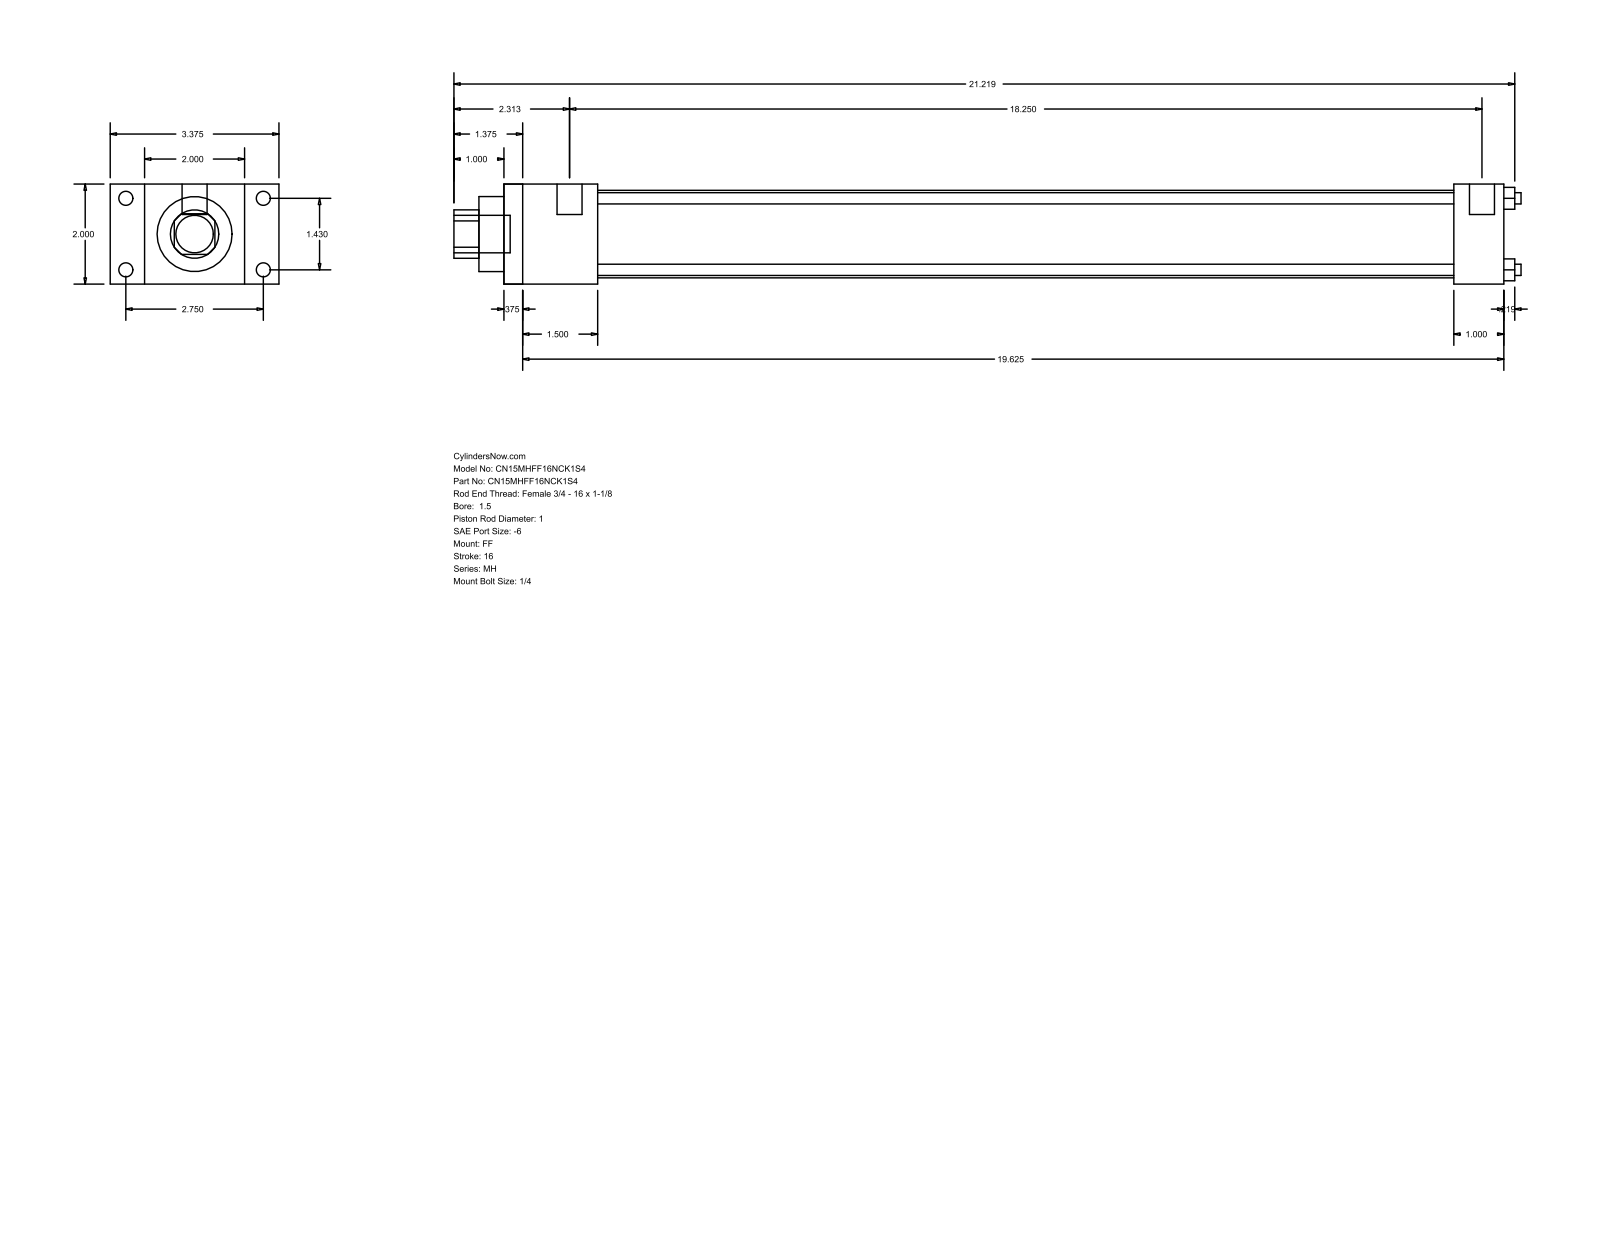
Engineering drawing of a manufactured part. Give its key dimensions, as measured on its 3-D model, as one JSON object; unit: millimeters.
{"part_name": "MH_FF__0150_1", "step_written_by": "GSSL Pune (CONFIG_CONTROL_DESIGN)", "units": "millimeters", "bodies": {"solids": 0, "faces": 92, "planar": 64, "cylindrical": 28, "other": 0}, "overall_size": [542.13, 85.72, 50.8], "round_holes": [[5.71, 4], [25.4, 1], [38.1, 1], [44.45, 1]], "round_bosses_or_shafts": [[7.14, 4], [5.56, 4], [12.7, 2], [19.05, 1]], "partial_cylinders_radius": [[12.29, 1]], "face_to_face_distances": [50.8, 508, 9.52, 498.48, 25.4, 17.46, 68.26, 47.63, 38.11, 460.37], "hole_center_spacings": [25.68, 36.32, 51.36]}
